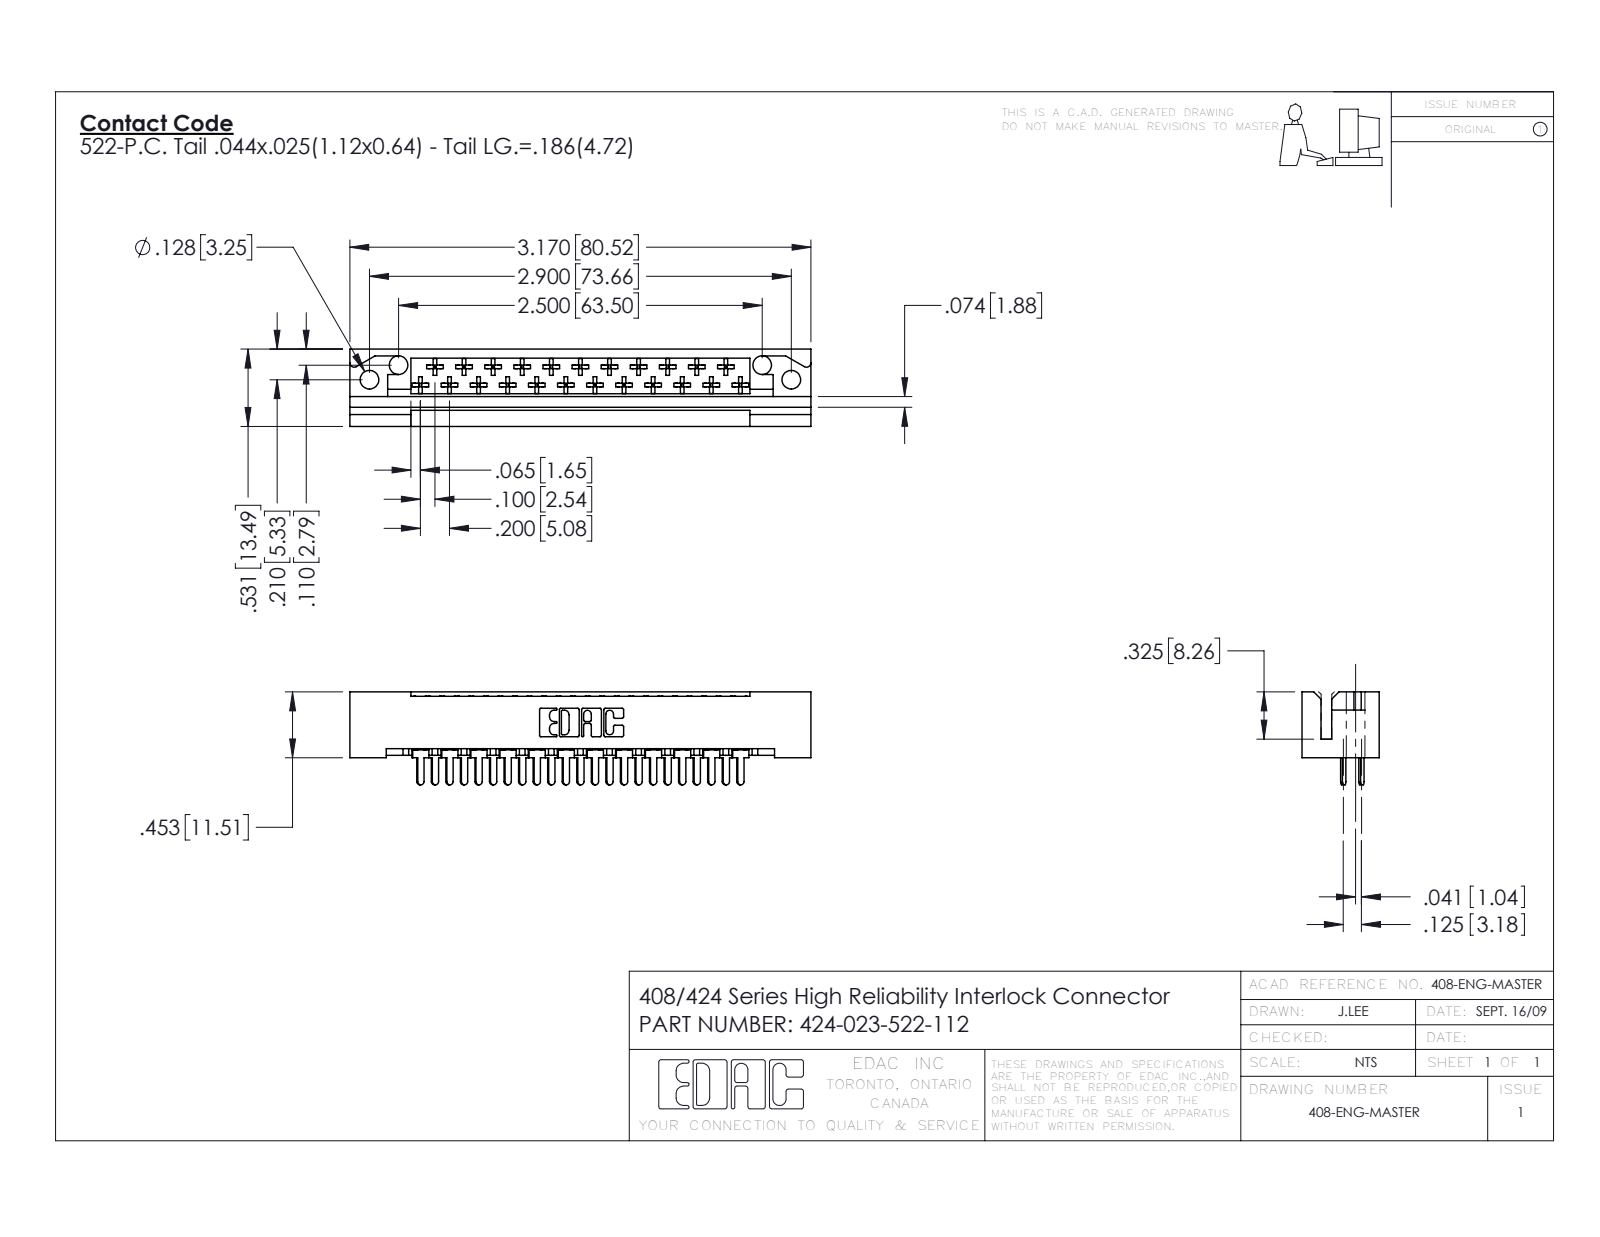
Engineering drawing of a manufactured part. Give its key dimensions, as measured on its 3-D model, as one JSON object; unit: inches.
{"part_name": "408-290-001_408-290-122; 424 Part_023; 424-023-522-112", "step_written_by": "SolidWorks 2016 (CONFIG_CONTROL_DESIGN)", "units": "inches", "bodies": {"solids": 24, "faces": 1410, "planar": 1055, "cylindrical": 263, "other": 92}, "overall_size": [3.17, 0.639, 0.531], "volume_in3": 0.536, "surface_area_in2": 16.5, "round_holes": [[0.128, 4]], "partial_cylinders_radius": [[0.01, 138], [0.02, 25], [0.022, 23], [0.01, 22], [0.007, 6], [0.031, 6], [0.026, 3], [0.03, 2]], "face_to_face_distances": [0.4, 0.025, 0.531, 0.125, 0.1, 0.131, 0.326, 0.074, 0.205, 0.091], "hole_center_spacings": [0.224, 2.702, 2.5, 2.9]}
